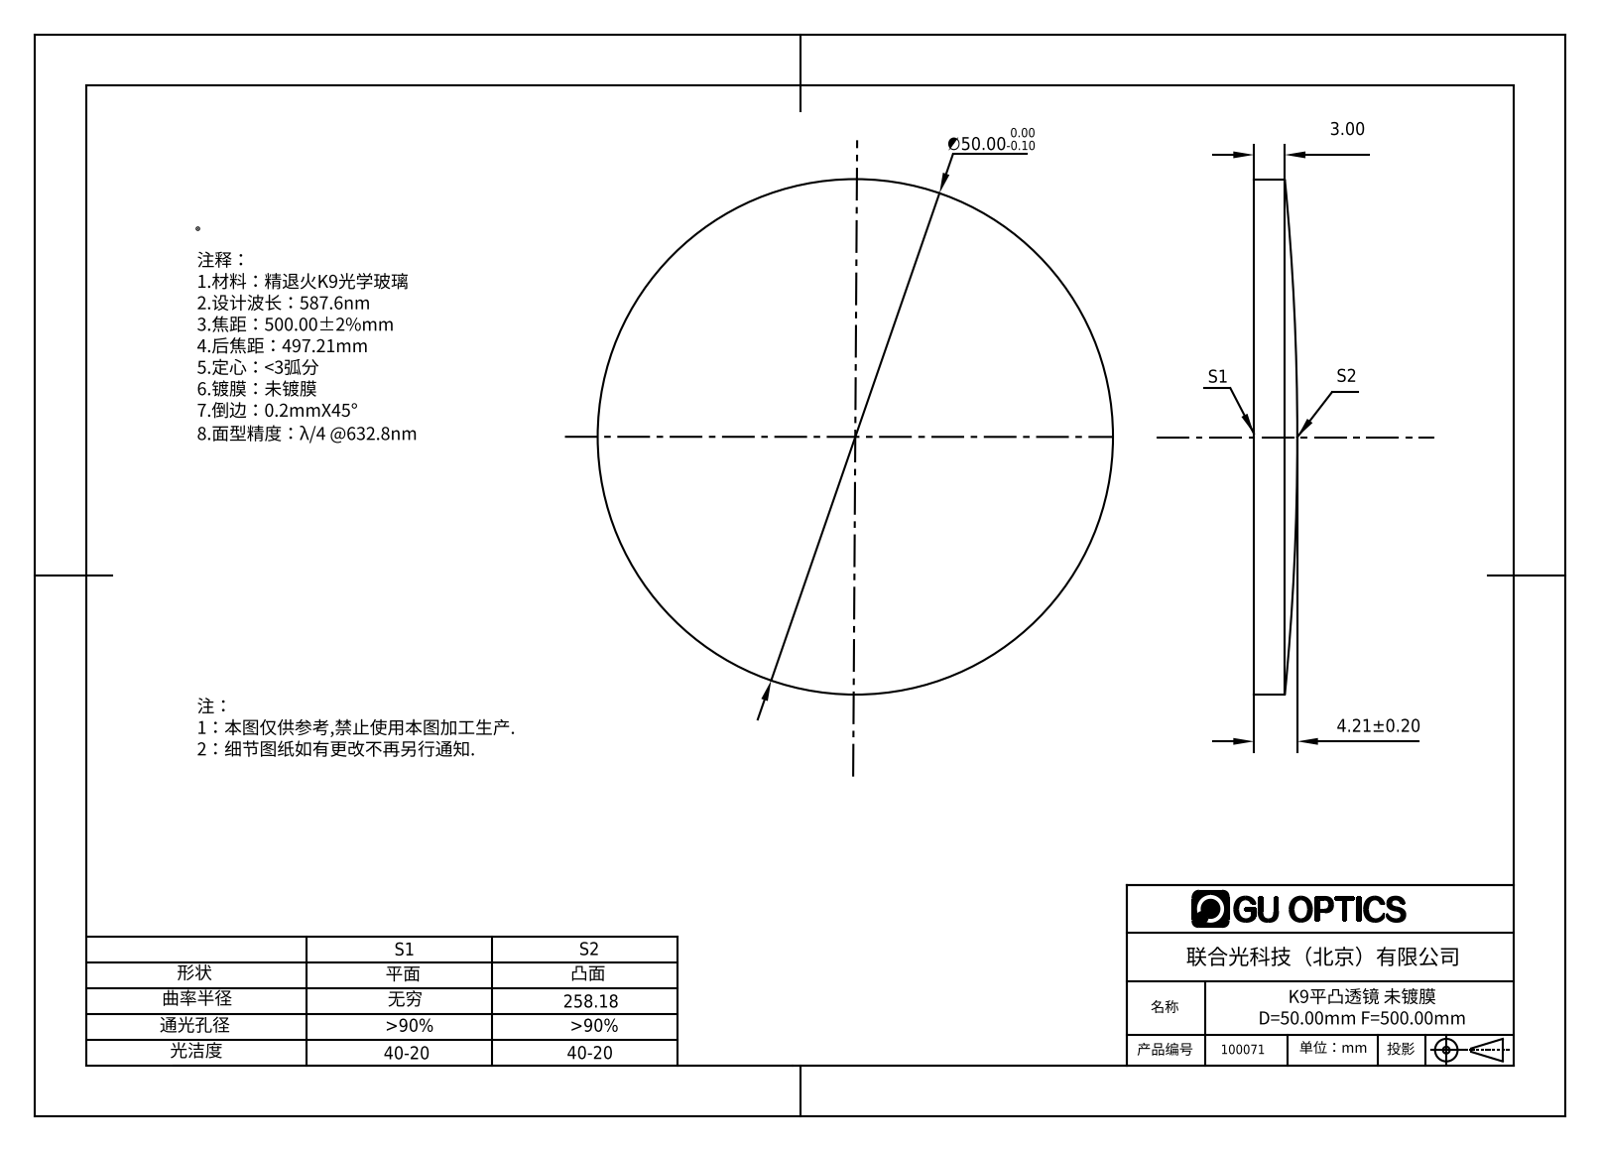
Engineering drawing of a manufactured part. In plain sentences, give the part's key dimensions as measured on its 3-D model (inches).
The part is named "100071". Its 3-D file was written by "SolidWorks 2016 (AUTOMOTIVE_DESIGN)". It is 1 solid with 5 faces: 1 planar, 2 cylindrical and 2 other. Overall it measures 1.969 by 1.969 by 0.166 inches. Its volume is 0.432 cubic inches and its surface area 6.825 square inches. Round bosses or shafts: 1 of diameter 1.969.
